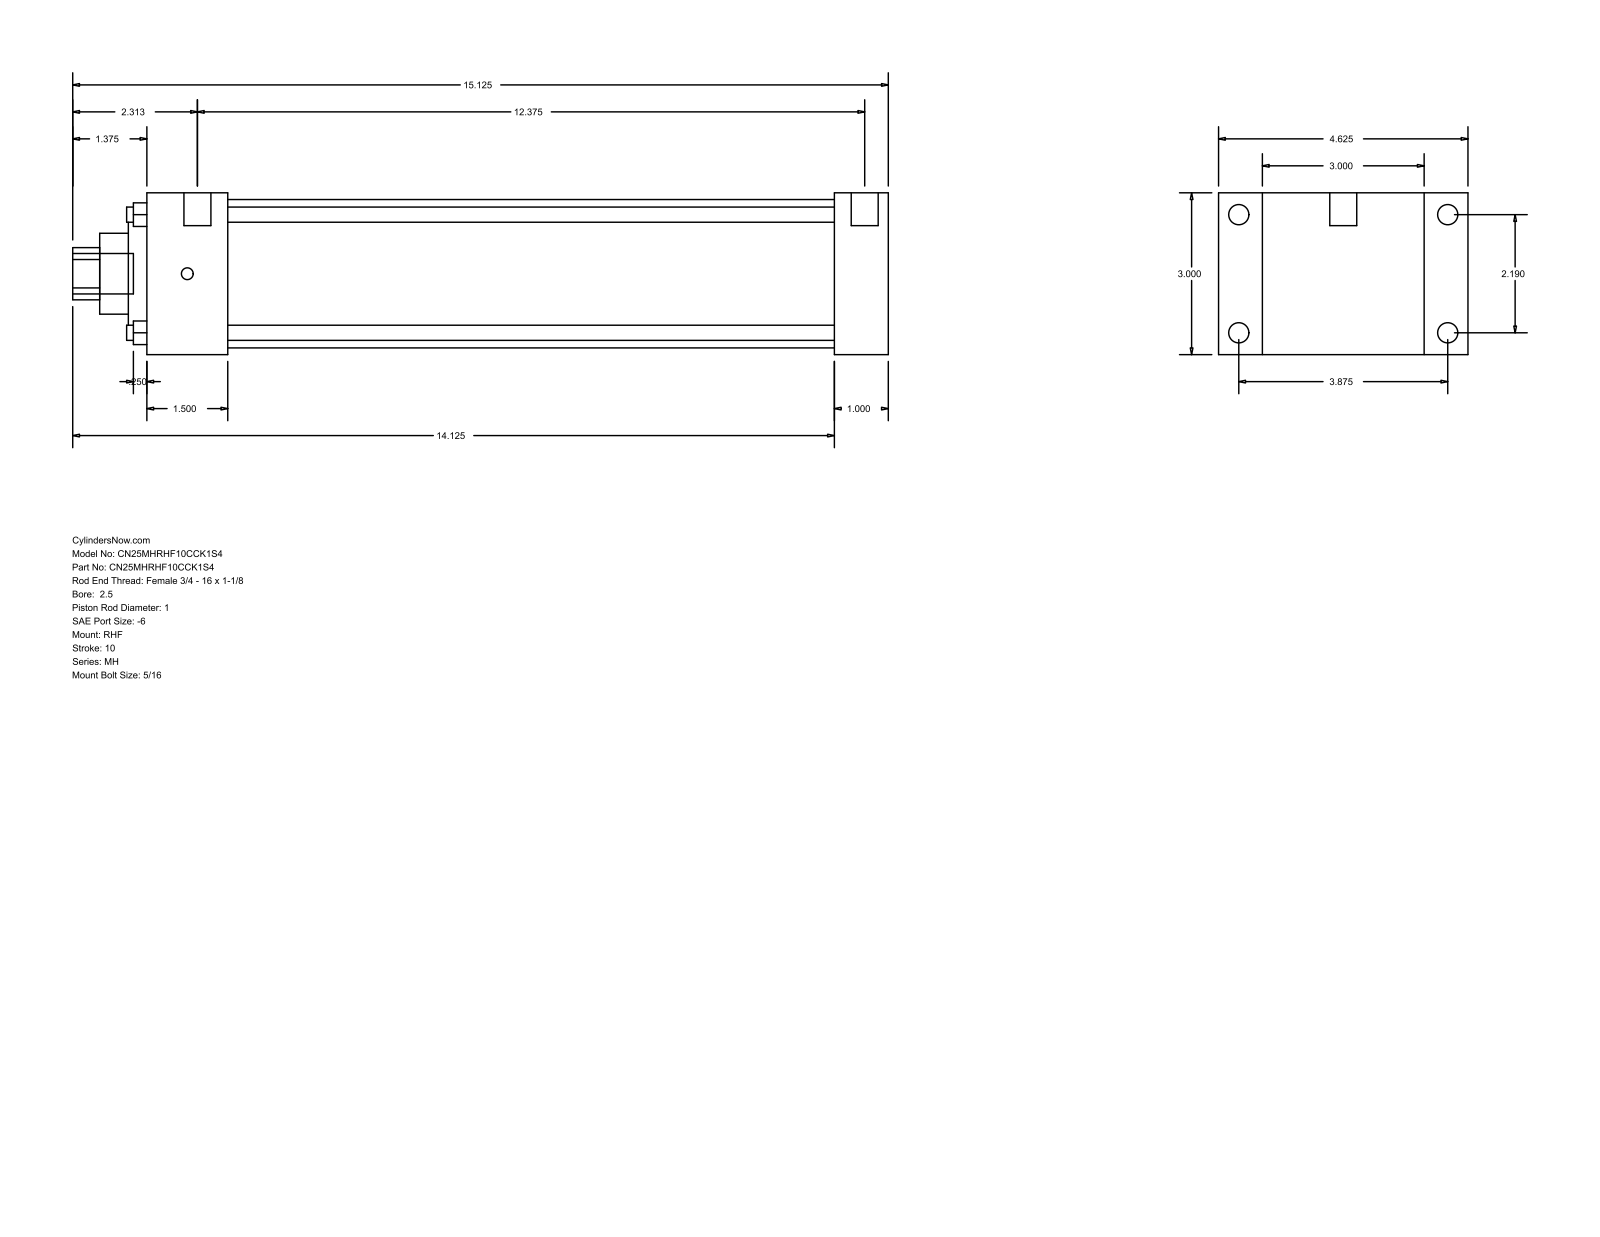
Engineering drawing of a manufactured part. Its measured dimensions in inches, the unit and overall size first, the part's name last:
Units: inches
Overall size (bounding box): 15.125 × 4.625 × 3
Round holes (diameter × count): ⌀0.281 ×4, ⌀1 ×1, ⌀1.5 ×1, ⌀2.375 ×1, ⌀2.75 ×1
Round bosses / shafts (diameter × count): ⌀0.375 ×4, ⌀0.219 ×4, ⌀0.5 ×2, ⌀0.75 ×1
Partial cylindrical surfaces — rounded edges, fillets, slot ends (radius × count): R0.484 ×1
Main face-to-face distances: 3, 1, 0.813, 3.813, 12.75, 13.75, 4.625, 1.5, 11.25, 12.25
Hole centre spacings: 1.548, 2.19, 3.097
Bodies: 0 solids, 90 faces (61 planar, 29 cylindrical, 0 other)
Part name (STEP PRODUCT): MH_RHF__0250_1
STEP written by: GSSL Pune (CONFIG_CONTROL_DESIGN)
